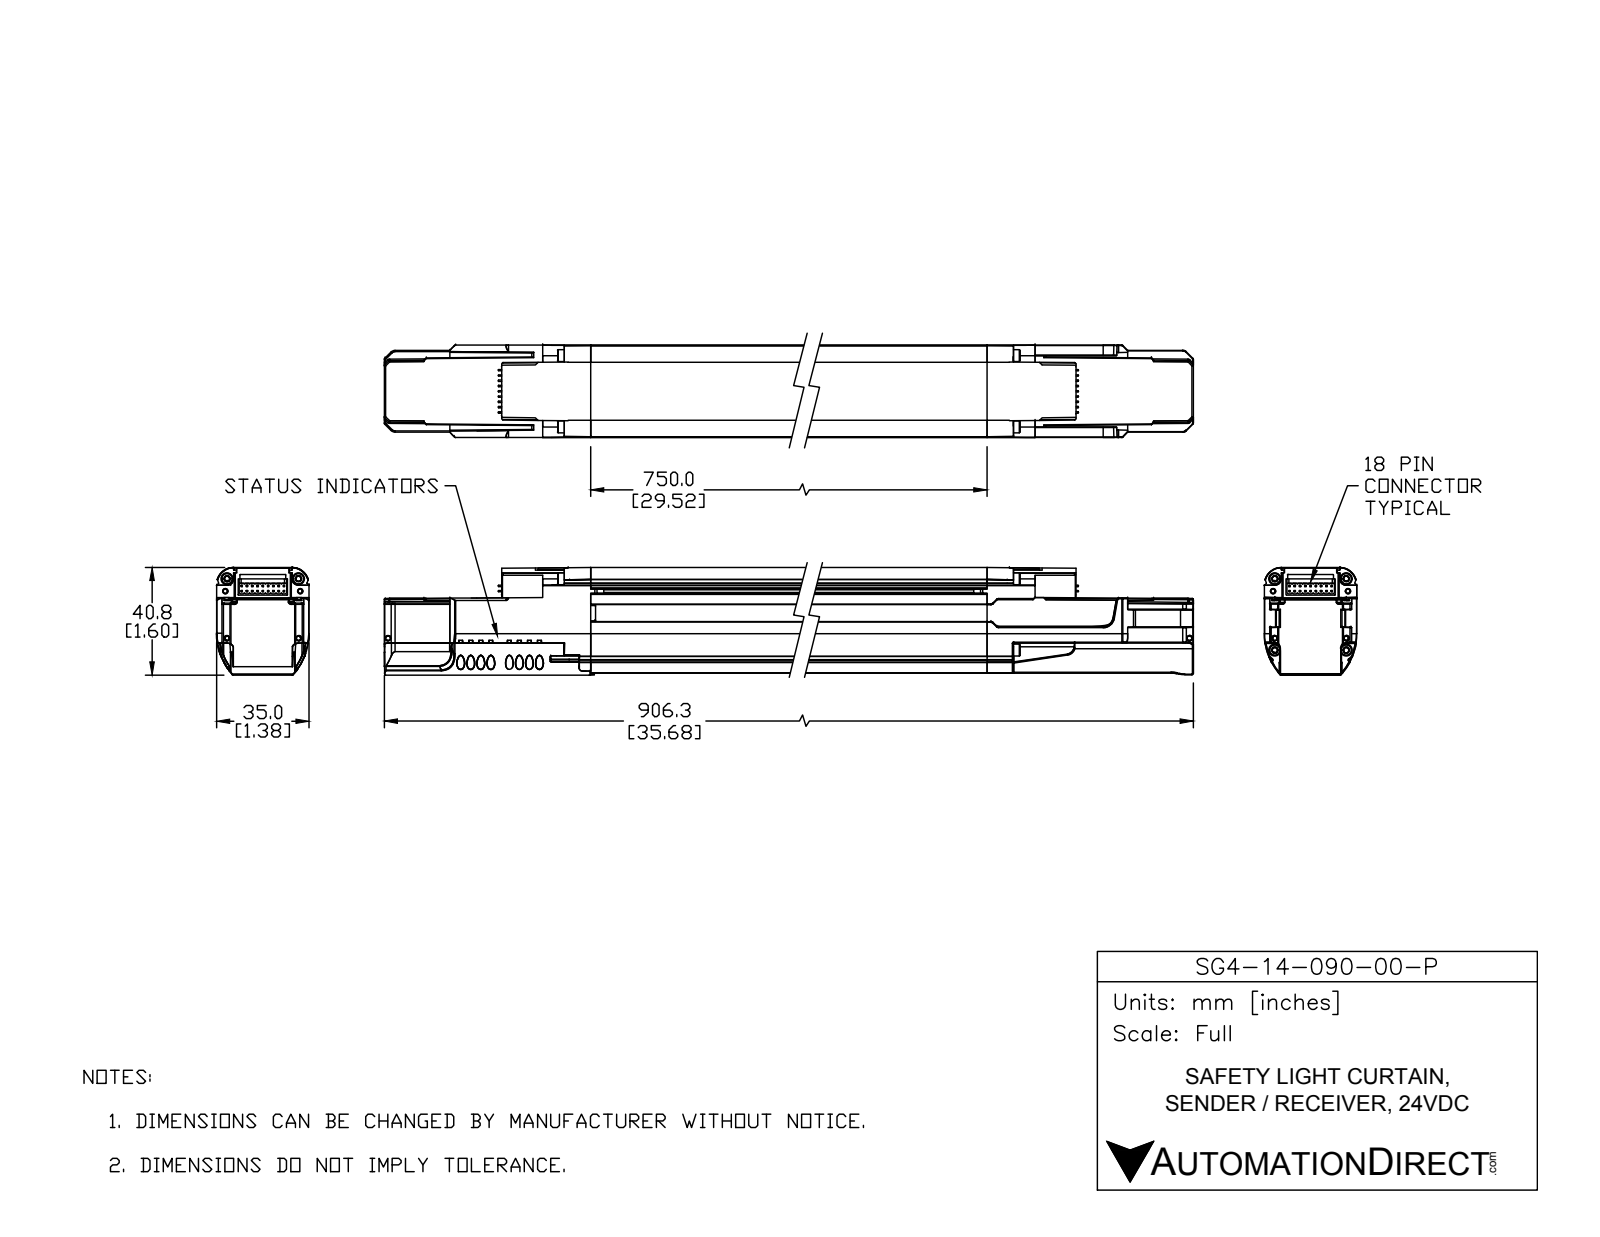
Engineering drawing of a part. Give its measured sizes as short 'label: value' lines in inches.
name: SG4-14-090-OO-P
written by: SolidWorks 2017 (AUTOMOTIVE_DESIGN)
unit: in
bodies: 16 solids, 534 faces (362 planar, 110 cylindrical, 62 other)
size: 35.673 × 2.58 × 2.023
volume: 67.38 in³; area: 381.2 in²
holes: 6× ⌀0.07, 4× ⌀0.1, 4× ⌀0.165, 4× ⌀0.209, 4× ⌀0.26, 1× ⌀0.065, 1× ⌀0.065
bosses: 4× ⌀0.394, 4× ⌀0.197
rounds: 16× R0.106, 8× R0.118, 4× R0.1, 4× R0.11, 2× R0.08, 2× R0.12, 2× R0.123, 2× R0.125
face distances: 0.06, 0.084, 0.024, 1.49, 1.466, 1.55, 1.057, 0.481, 0.985, 1.009
hole spacings: 0.569, 27.945, 0.02, 0.204, 0.207, 0.207, 0.227, 0.71
